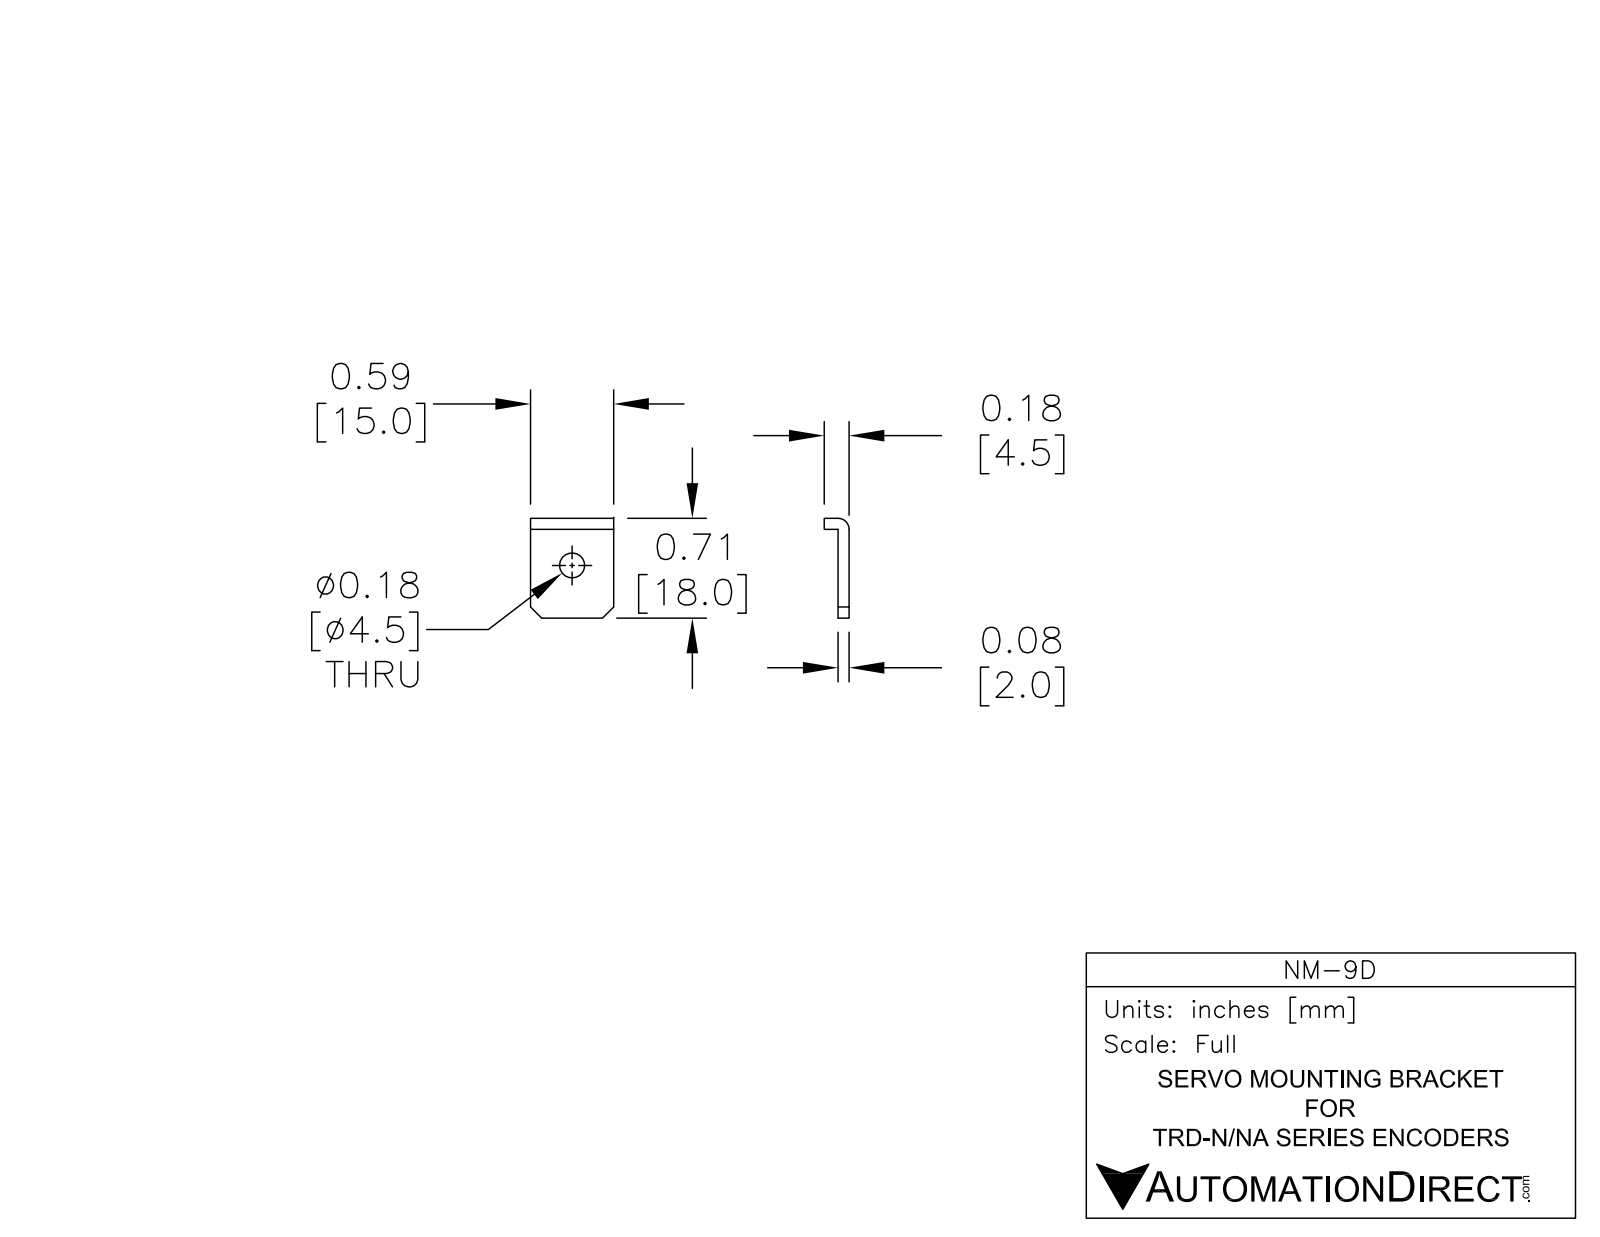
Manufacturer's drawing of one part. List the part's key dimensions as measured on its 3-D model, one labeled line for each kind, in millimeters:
Part name (STEP PRODUCT): NM-9
STEP written by: PRO/ENGINEER BY PARAMETRIC TECHNOLOGY CORPORATION, 2010020 (AUTOMOTIVE_DESIGN_CC2)
Units: millimetres
Bodies: 1 solid, 13 faces (10 planar, 3 cylindrical, 0 other)
Overall size (bounding box): 18 × 15 × 4.6
Volume: 565 mm³ · Surface area: 730 mm²
Round holes (diameter × count): ⌀4.5 ×1
Partial cylindrical surfaces — rounded edges, fillets, slot ends (radius × count): R2 ×1
Main face-to-face distances: 2, 15, 2.6, 4.6, 18, 16
